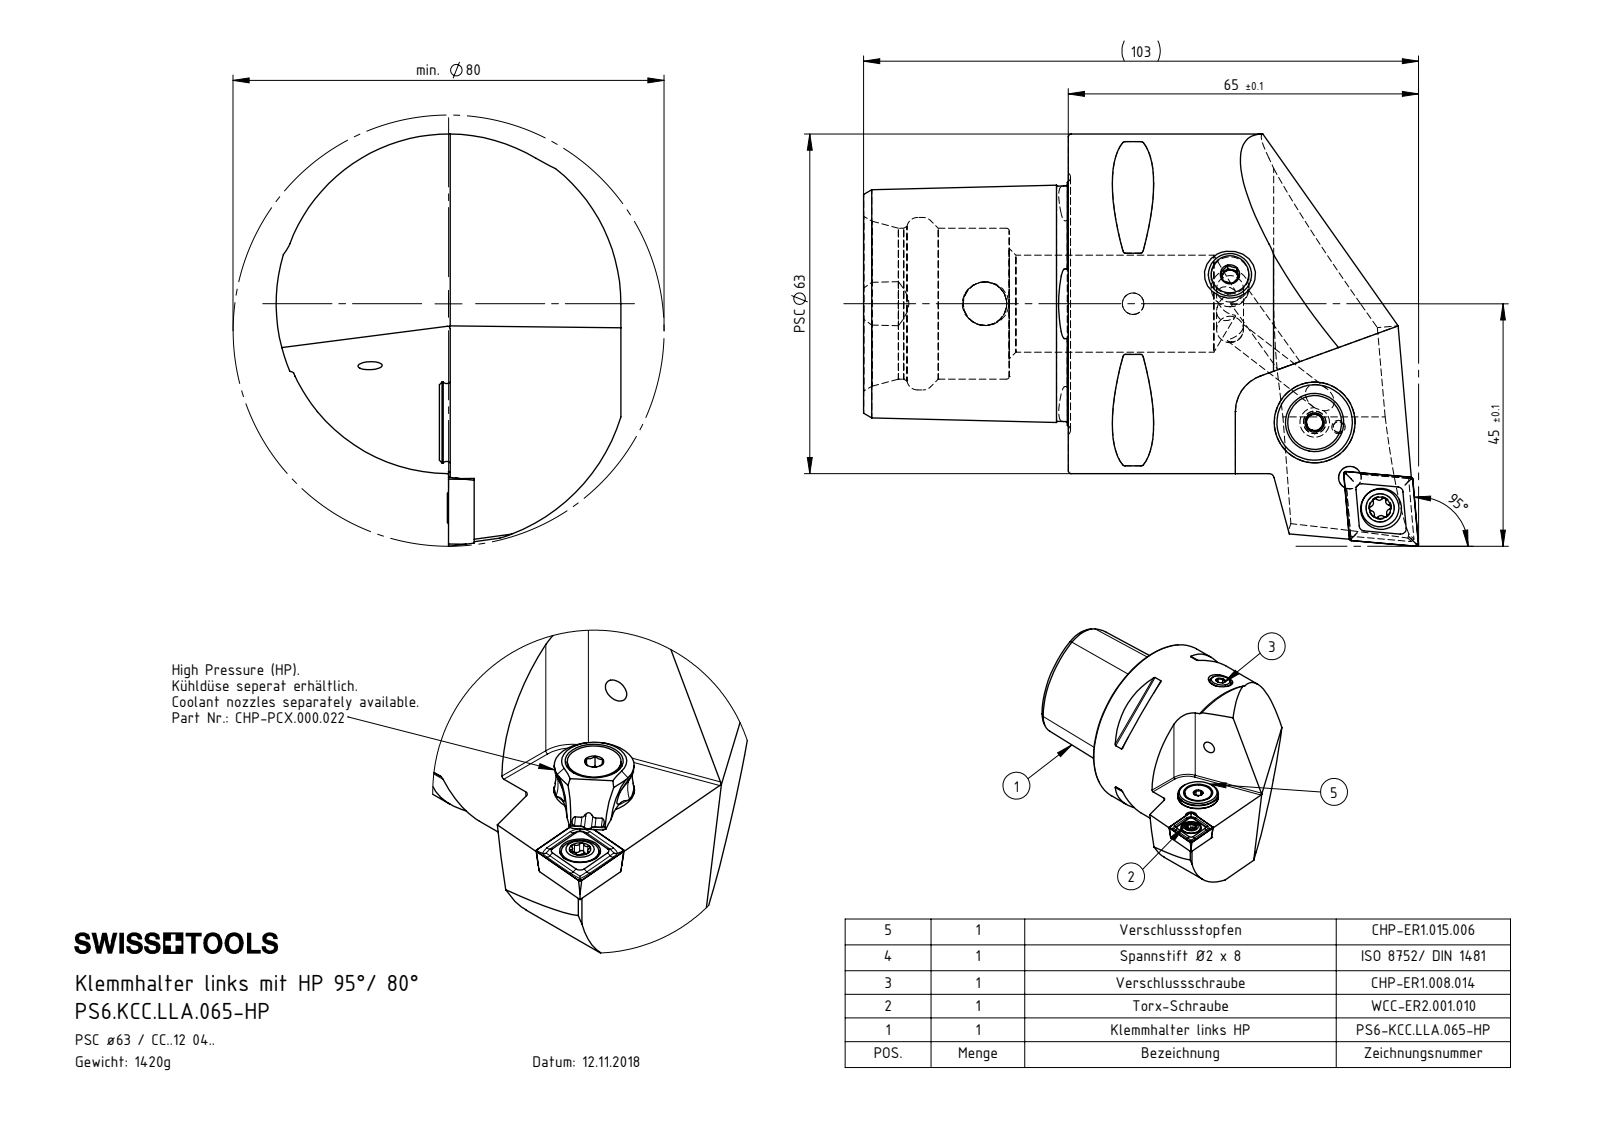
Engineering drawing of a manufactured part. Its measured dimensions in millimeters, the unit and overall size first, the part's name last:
Units: millimetres
Overall size (bounding box): 103 × 76.5 × 64
Round holes (diameter × count): ⌀4.2 ×4, ⌀5 ×2, ⌀1.2 ×1, ⌀2 ×1, ⌀2.5 ×1, ⌀3 ×1, ⌀4 ×1, ⌀5.2 ×1, ⌀5.5 ×1, ⌀7 ×1, ⌀7.6 ×1, ⌀8.1 ×1
Round bosses / shafts (diameter × count): ⌀5 ×2, ⌀63 ×1, ⌀15 ×1, ⌀13.4 ×1, ⌀10 ×1, ⌀8 ×1, ⌀7 ×1, ⌀5.5 ×1
Partial cylindrical surfaces — rounded edges, fillets, slot ends (radius × count): R0.5 ×10, R0.39 ×6, R0.69 ×3, R0.69 ×3, R6 ×1, R7 ×1, R32 ×1, R34 ×1
Main face-to-face distances: 38, 31.7, 24.88, 27.2, 4.5, 27, 11, 27.24, 4.46, 69
Hole centre spacings: 4.49, 7.93, 8.2, 9.61, 12.14, 16.86, 17.11, 19.96
Volume: 181 467 mm³ · Surface area: 32 420 mm²
Bodies: 8 solids, 371 faces (88 planar, 99 cylindrical, 184 other)
Part name (STEP PRODUCT): CHP-ER1.015.006; CCMT120404; CHP-ER1.015.006_A; ISO 8752 2x8 (+6 more)
STEP written by: SolidWorks 2017 (AUTOMOTIVE_DESIGN)
